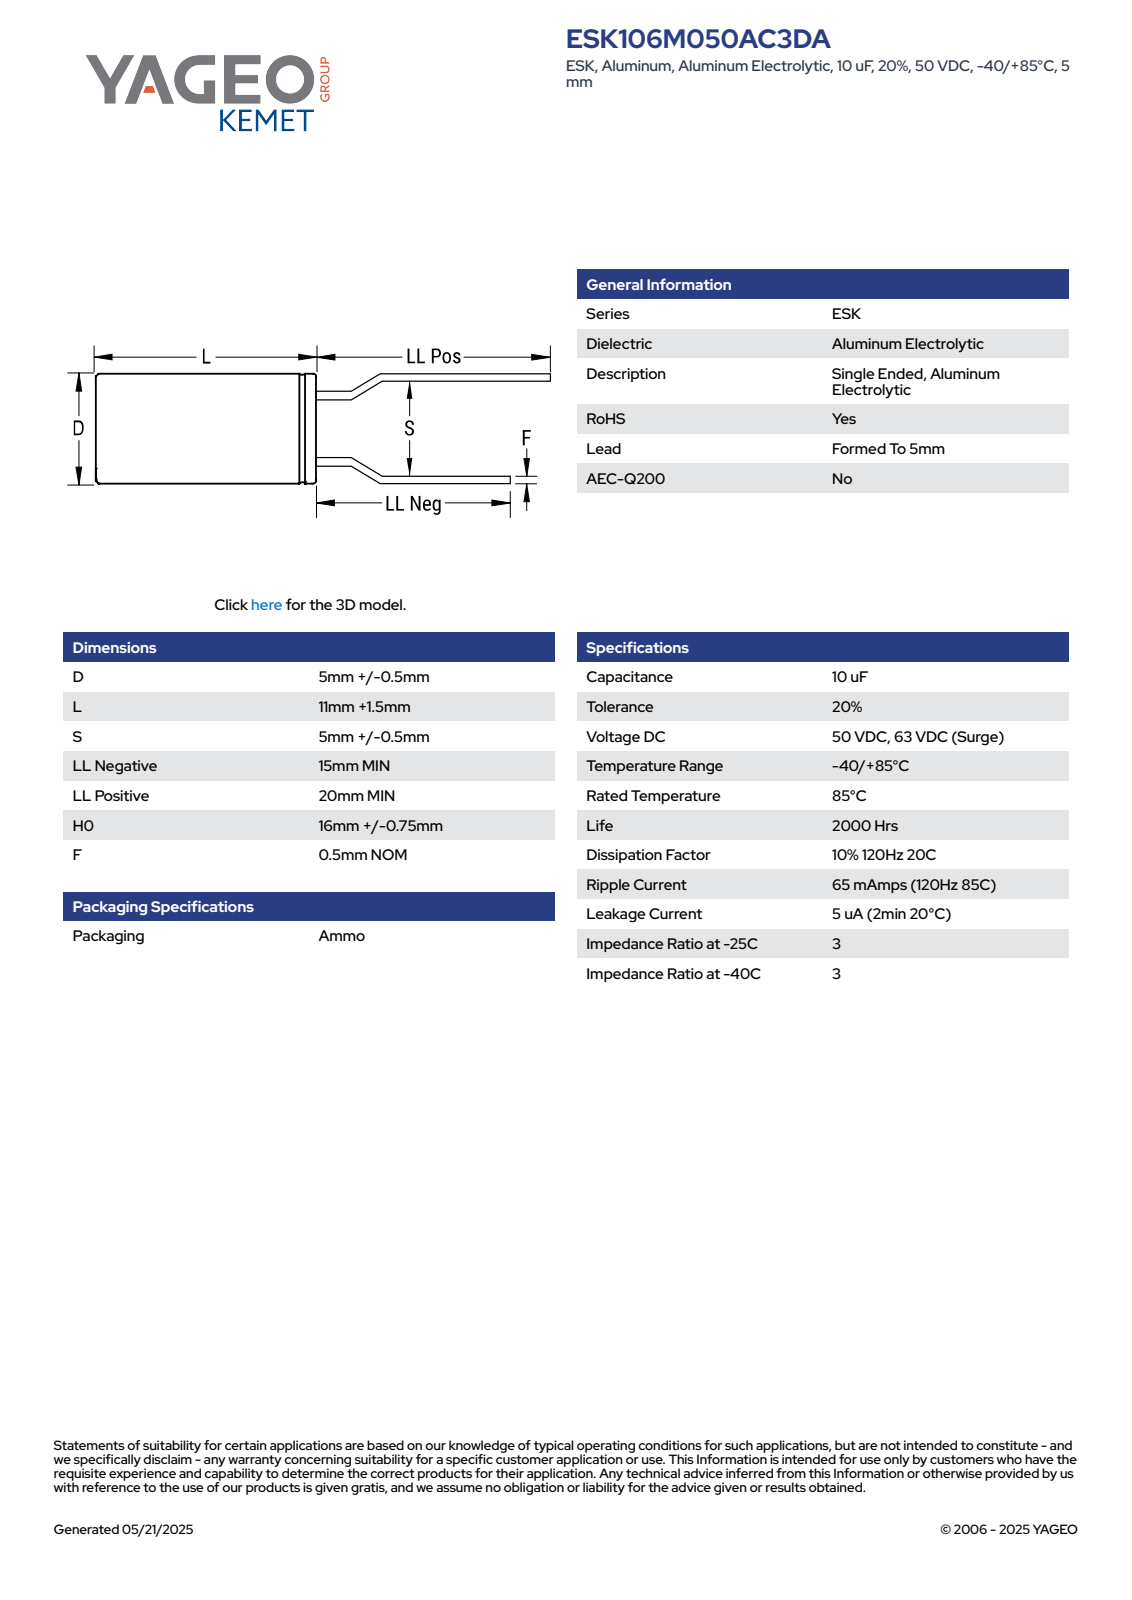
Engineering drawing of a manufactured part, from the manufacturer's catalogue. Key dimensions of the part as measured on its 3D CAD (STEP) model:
Part name (STEP PRODUCT): CAR_KTRF5_5X11_D5.5L12.5S5F0.5
STEP written by: SolidWorks 2014 (AUTOMOTIVE_DESIGN)
Units: millimetres
Bodies: 4 solids, 81 faces (61 planar, 16 cylindrical, 4 other)
Overall size (bounding box): 25 × 5.5 × 5.5
Volume: 300 mm³ · Surface area: 312 mm²
Round bosses / shafts (diameter × count): ⌀0.5 ×6, ⌀5.5 ×1
Main face-to-face distances: 12.5, 12.51, 25.01, 25, 0.65, 0.66, 2.67, 0.4, 1.35, 2.01
